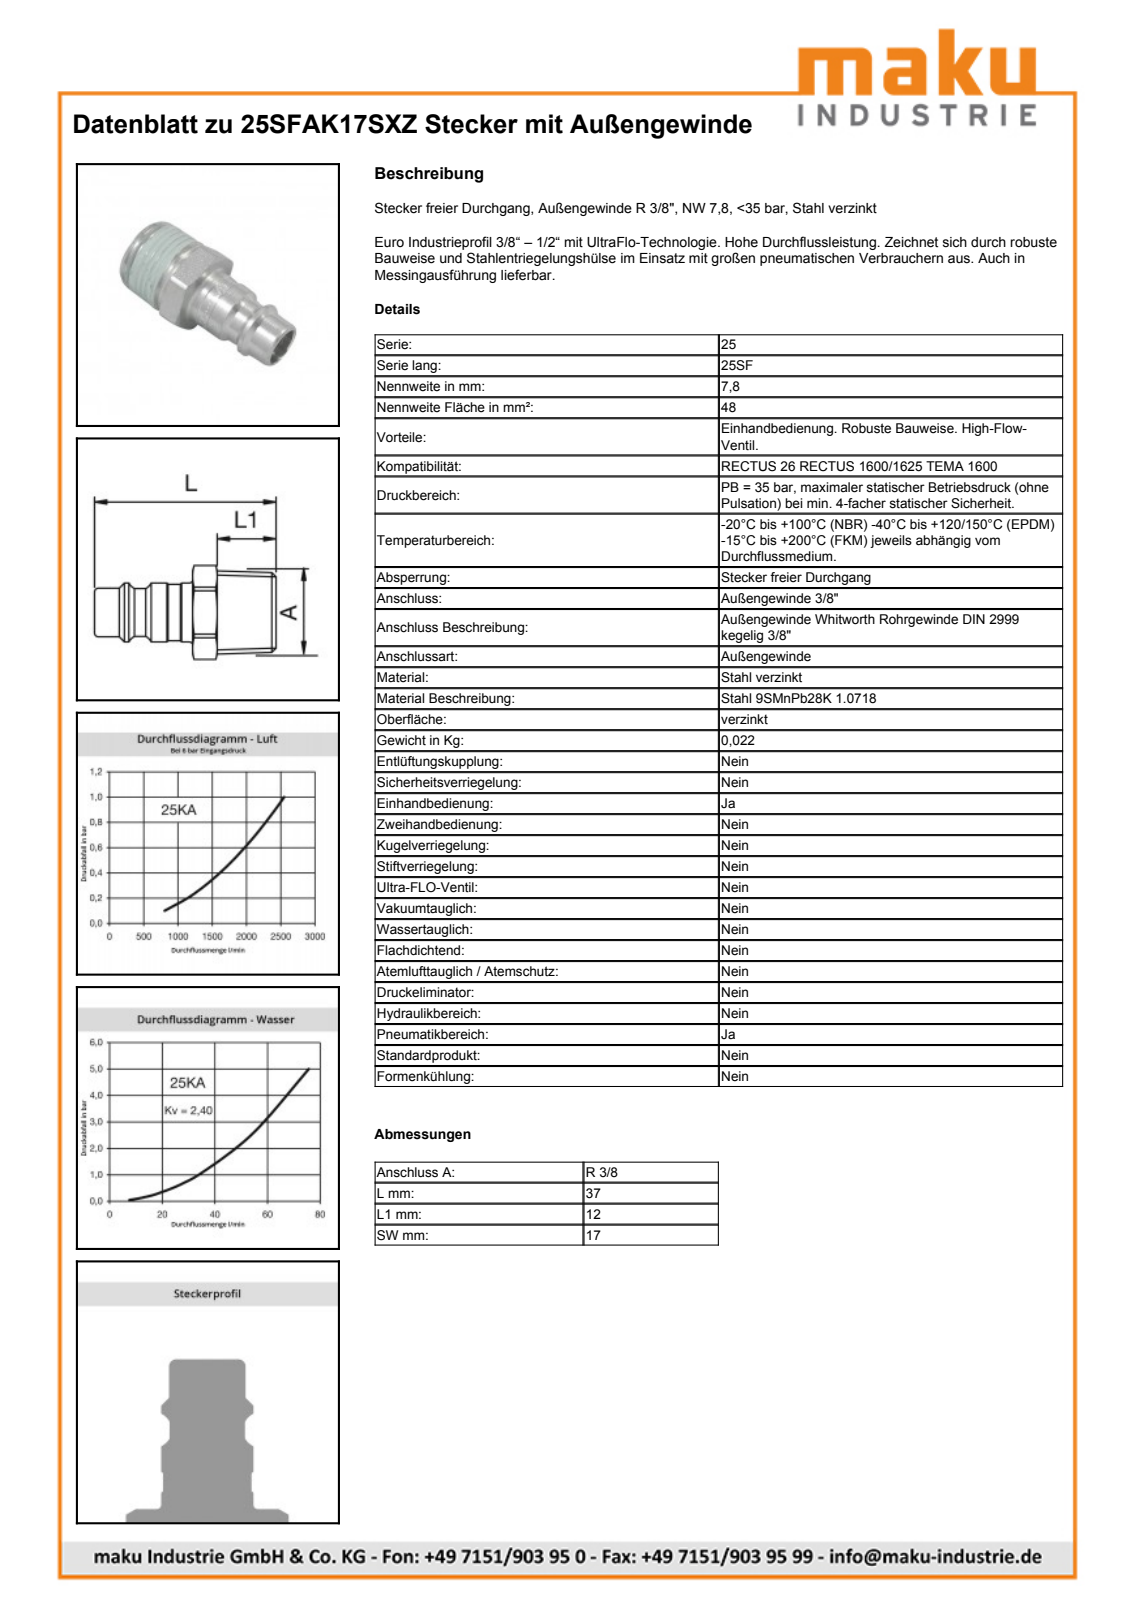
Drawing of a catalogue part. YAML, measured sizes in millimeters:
part_name: "D106827"
step_written_by: "Autodesk Inventor 2013 (AUTOMOTIVE_DESIGN)"
units: millimeters
bodies: {solids: 1, faces: 41, planar: 9, cylindrical: 12, other: 20}
overall_size: [37, 19.15, 17]
volume: 3152
surface_area: 3000
round_holes:
  - {diameter: 7.85, count: 1}
  - {diameter: 11.5, count: 1}
round_bosses_or_shafts:
  - {diameter: 12, count: 1}
  - {diameter: 9.9, count: 1}
  - {diameter: 9.75, count: 1}
partial_cylinders:
  - {radius: 9.57, count: 1}
face_to_face_distances: [17, 20, 37]
